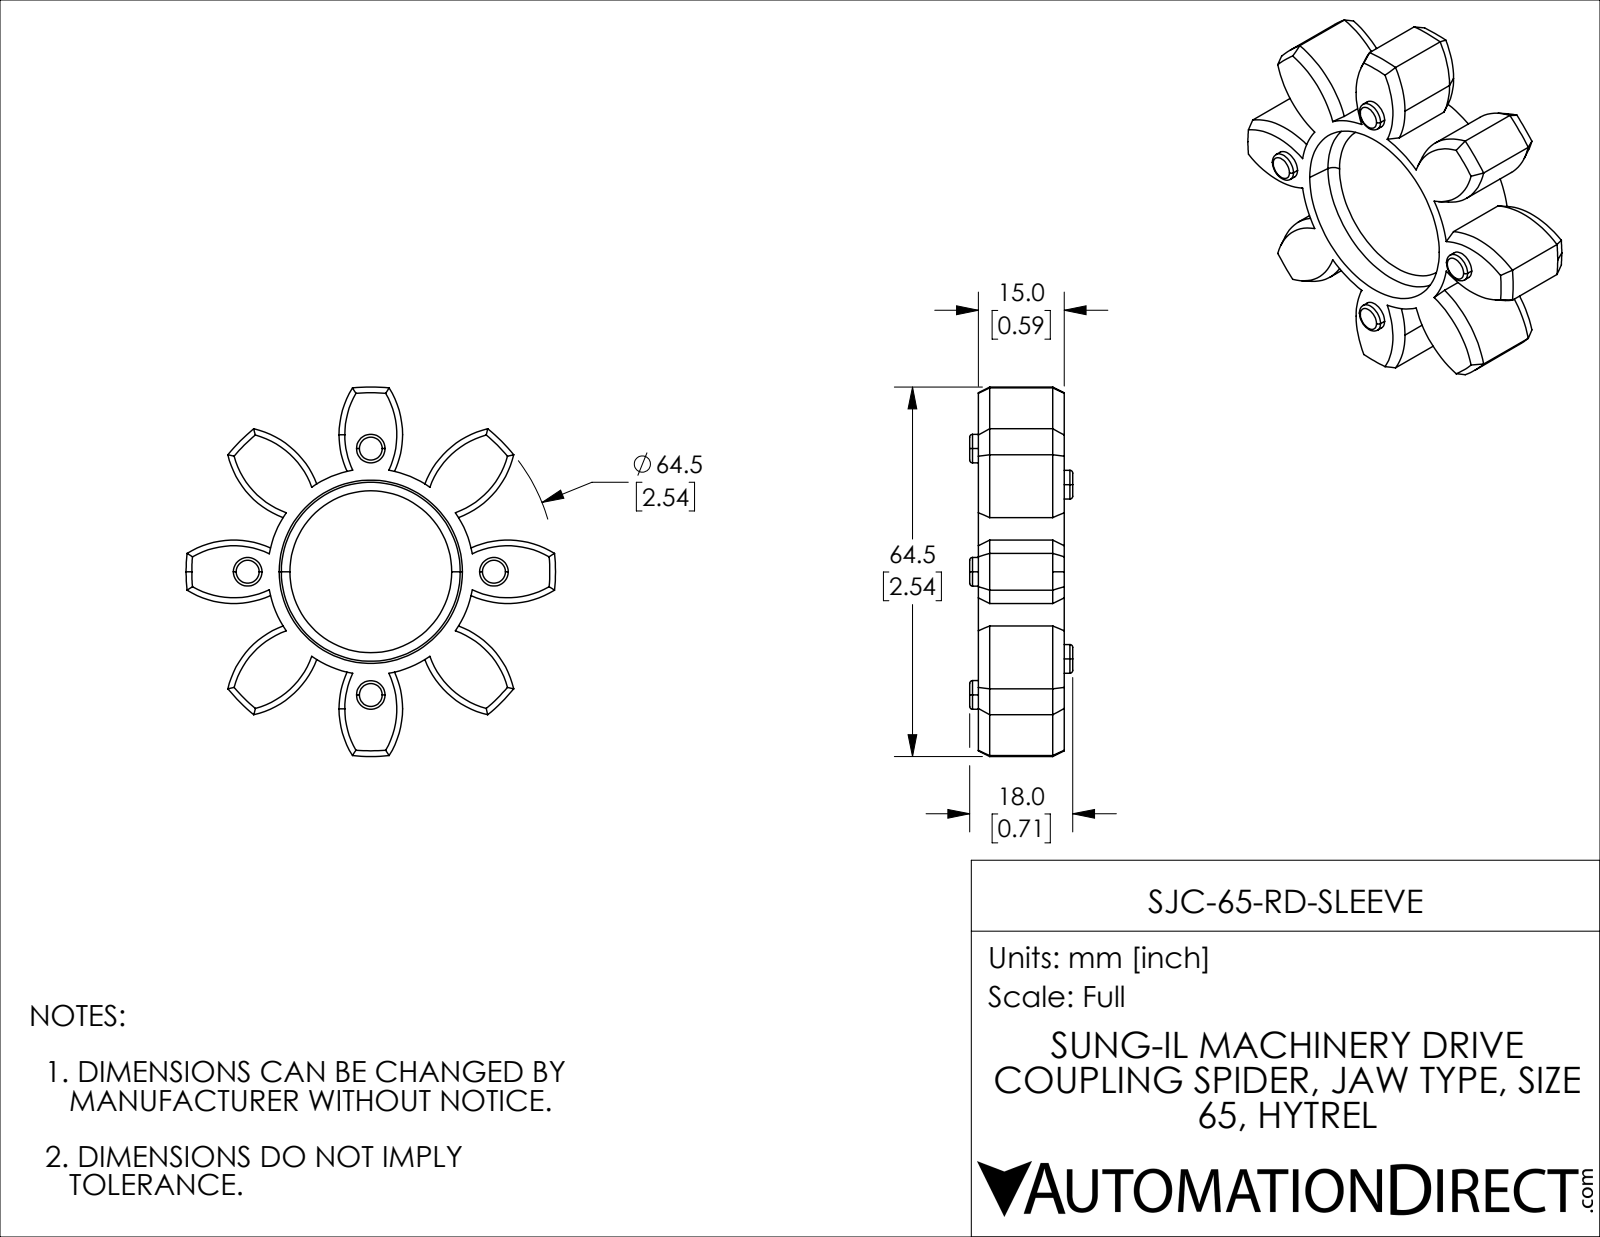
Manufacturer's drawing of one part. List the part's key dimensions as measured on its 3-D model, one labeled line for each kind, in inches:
Part name (STEP PRODUCT): SJC-65-RD-SLEEVE
STEP written by: SolidWorks 2021 (CONFIG_CONTROL_DESIGN)
Units: inches
Bodies: 1 solid, 141 faces (12 planar, 51 cylindrical, 78 other)
Overall size (bounding box): 2.539 × 2.539 × 0.709
Volume: 1.428 in³ · Surface area: 15.51 in²
Round bosses / shafts (diameter × count): ⌀0.197 ×8
Partial cylindrical surfaces — rounded edges, fillets, slot ends (radius × count): R0.608 ×8, R0.709 ×1, R1.27 ×1
Main face-to-face distances: 0.217, 0.374, 0.591, 0.157, 0.059, 0.276, 0.433, 0.65, 0.709
